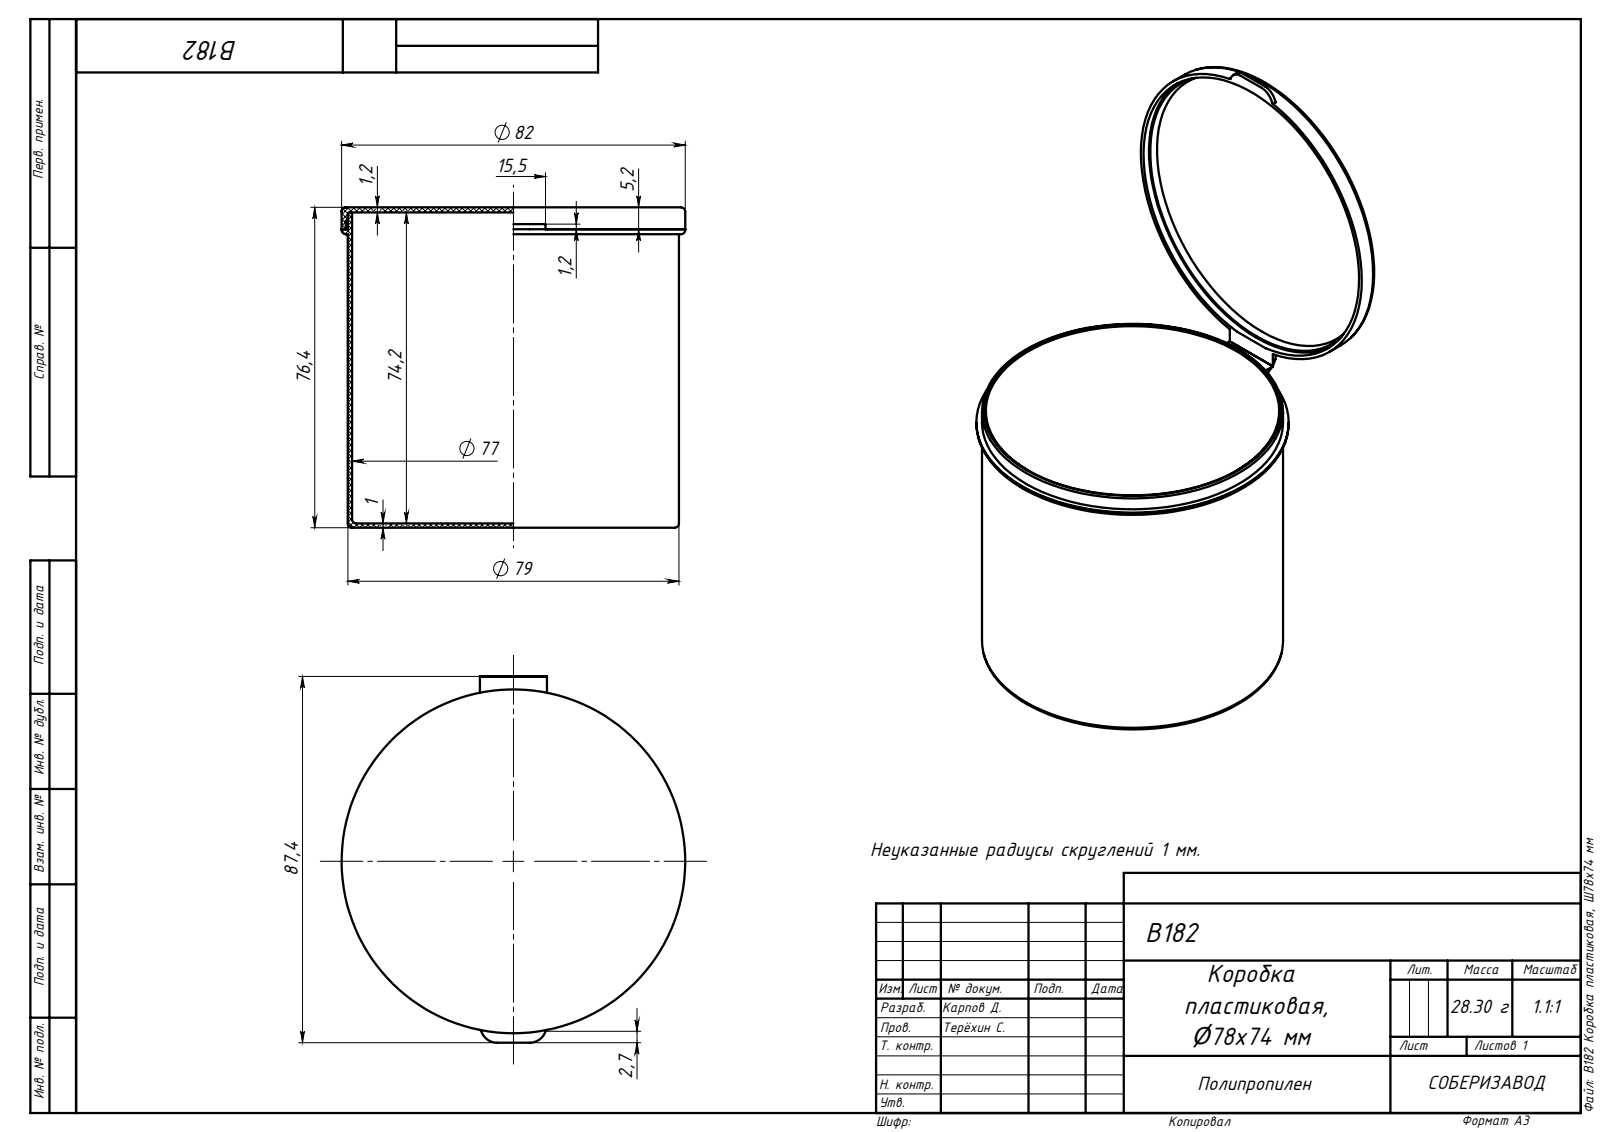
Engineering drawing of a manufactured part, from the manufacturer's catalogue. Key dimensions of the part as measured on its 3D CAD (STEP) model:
Part name (STEP PRODUCT): B182 Коробка пластиковая, O78x74 мм; B182 Емкость; B182 Крышка
STEP written by: SolidWorks 2020 (AUTOMOTIVE_DESIGN)
Units: millimetres
Bodies: 3 solids, 62 faces (23 planar, 19 cylindrical, 20 other)
Overall size (bounding box): 87.36 × 82 × 76.4
Volume: 31 163 mm³ · Surface area: 59 853 mm²
Round holes (diameter × count): ⌀77 ×1, ⌀80 ×1
Round bosses / shafts (diameter × count): ⌀82 ×1, ⌀79 ×1
Partial cylindrical surfaces — rounded edges, fillets, slot ends (radius × count): R0.5 ×2, R4 ×2, R0.1 ×1
Main face-to-face distances: 1.2, 75.2, 76.4, 1, 74.2, 75.4, 5.2, 70.2, 71.2, 4
